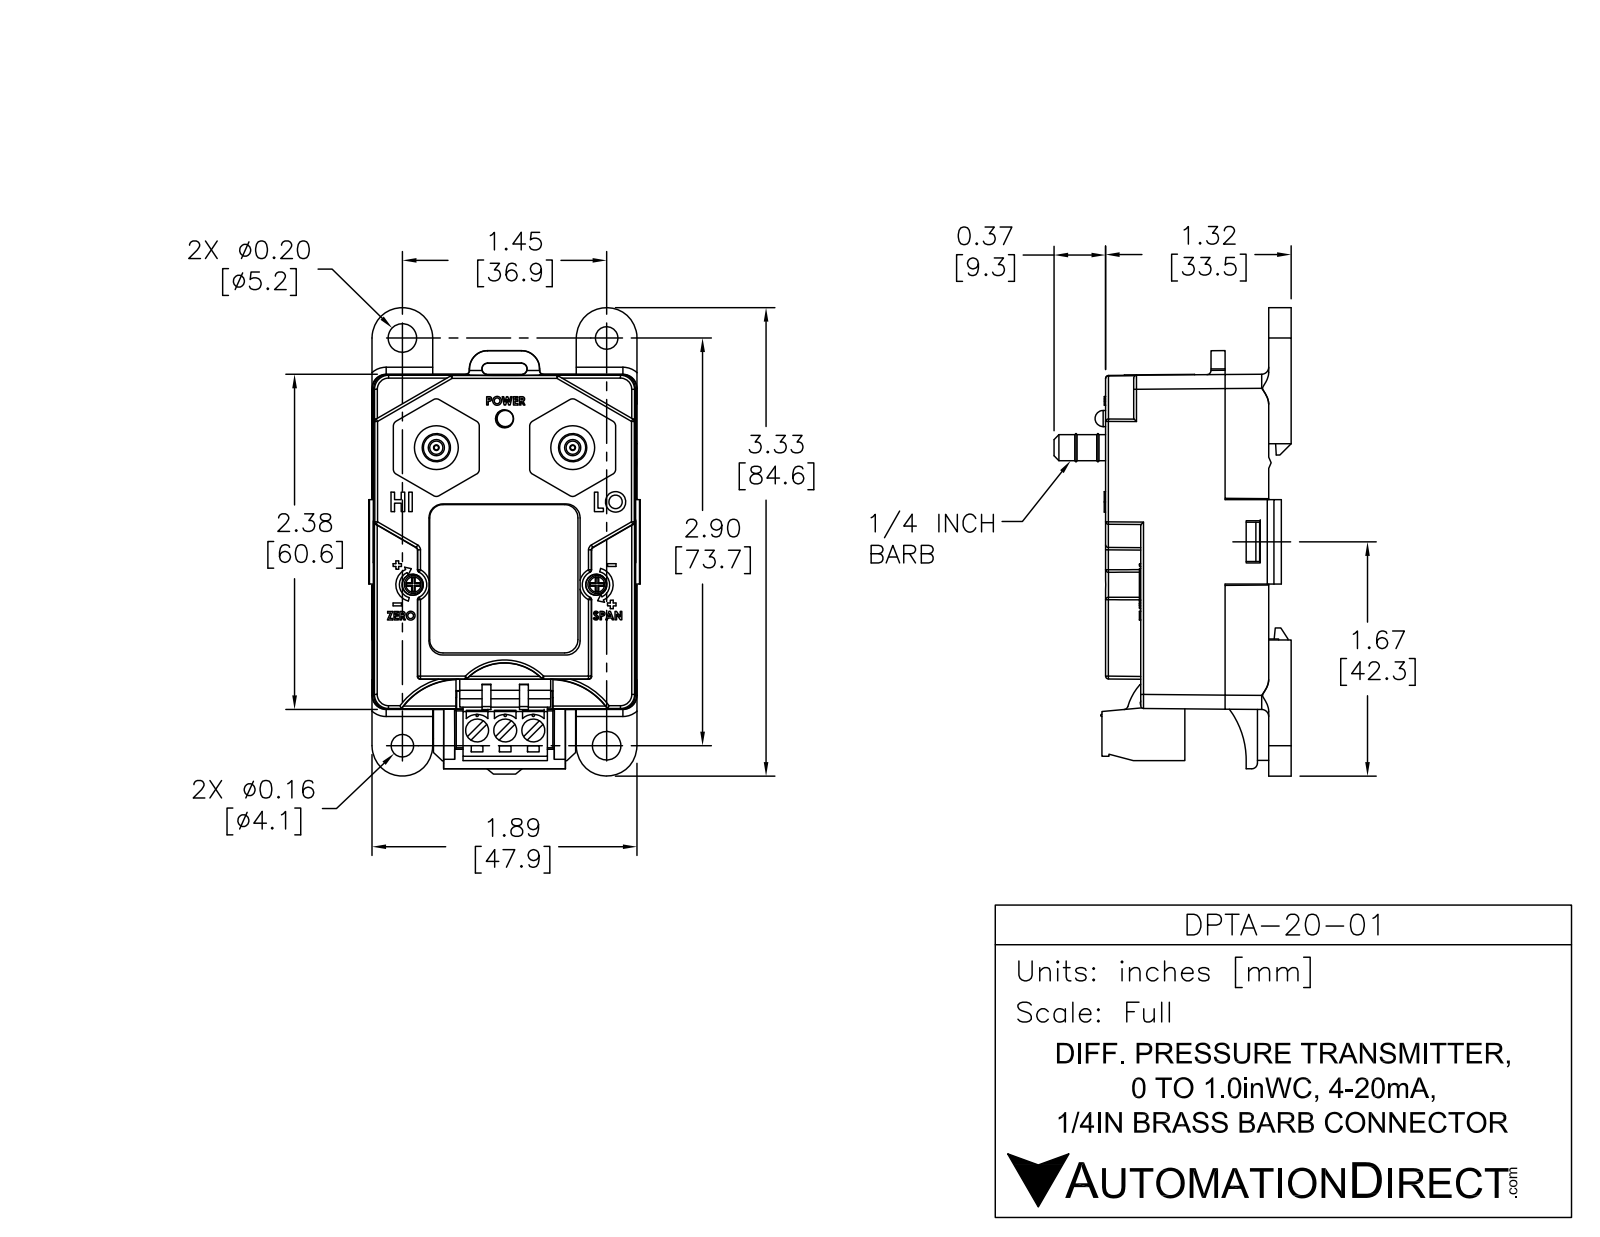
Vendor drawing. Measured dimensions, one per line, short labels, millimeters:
name: DPTA-20-01
written by: SolidWorks 2011 (AUTOMOTIVE_DESIGN)
unit: mm
bodies: 11 solids, 448 faces (354 planar, 85 cylindrical, 9 other)
size: 85.01 × 49.76 × 43.1
volume: 29 684 mm³; area: 34 743 mm²
holes: 7× ⌀4, 2× ⌀2.5, 2× ⌀5.12, 1× ⌀3.1
bosses: 3× ⌀5, 3× ⌀3.5, 3× ⌀3.5, 2× ⌀8, 2× ⌀4.75, 1× ⌀3
rounds: 12× R3, 4× R2, 4× R5.5, 2× R0.99, 2× R1.06, 2× R1.12, 2× R2.38, 2× R3.25
face distances: 1, 1.9, 4, 29.1, 0.5, 46.9, 5.9, 5, 33.1, 27.2
hole spacings: 13.55, 20.73, 23.37, 24.92, 29.43, 34.46, 36.67, 38.22
